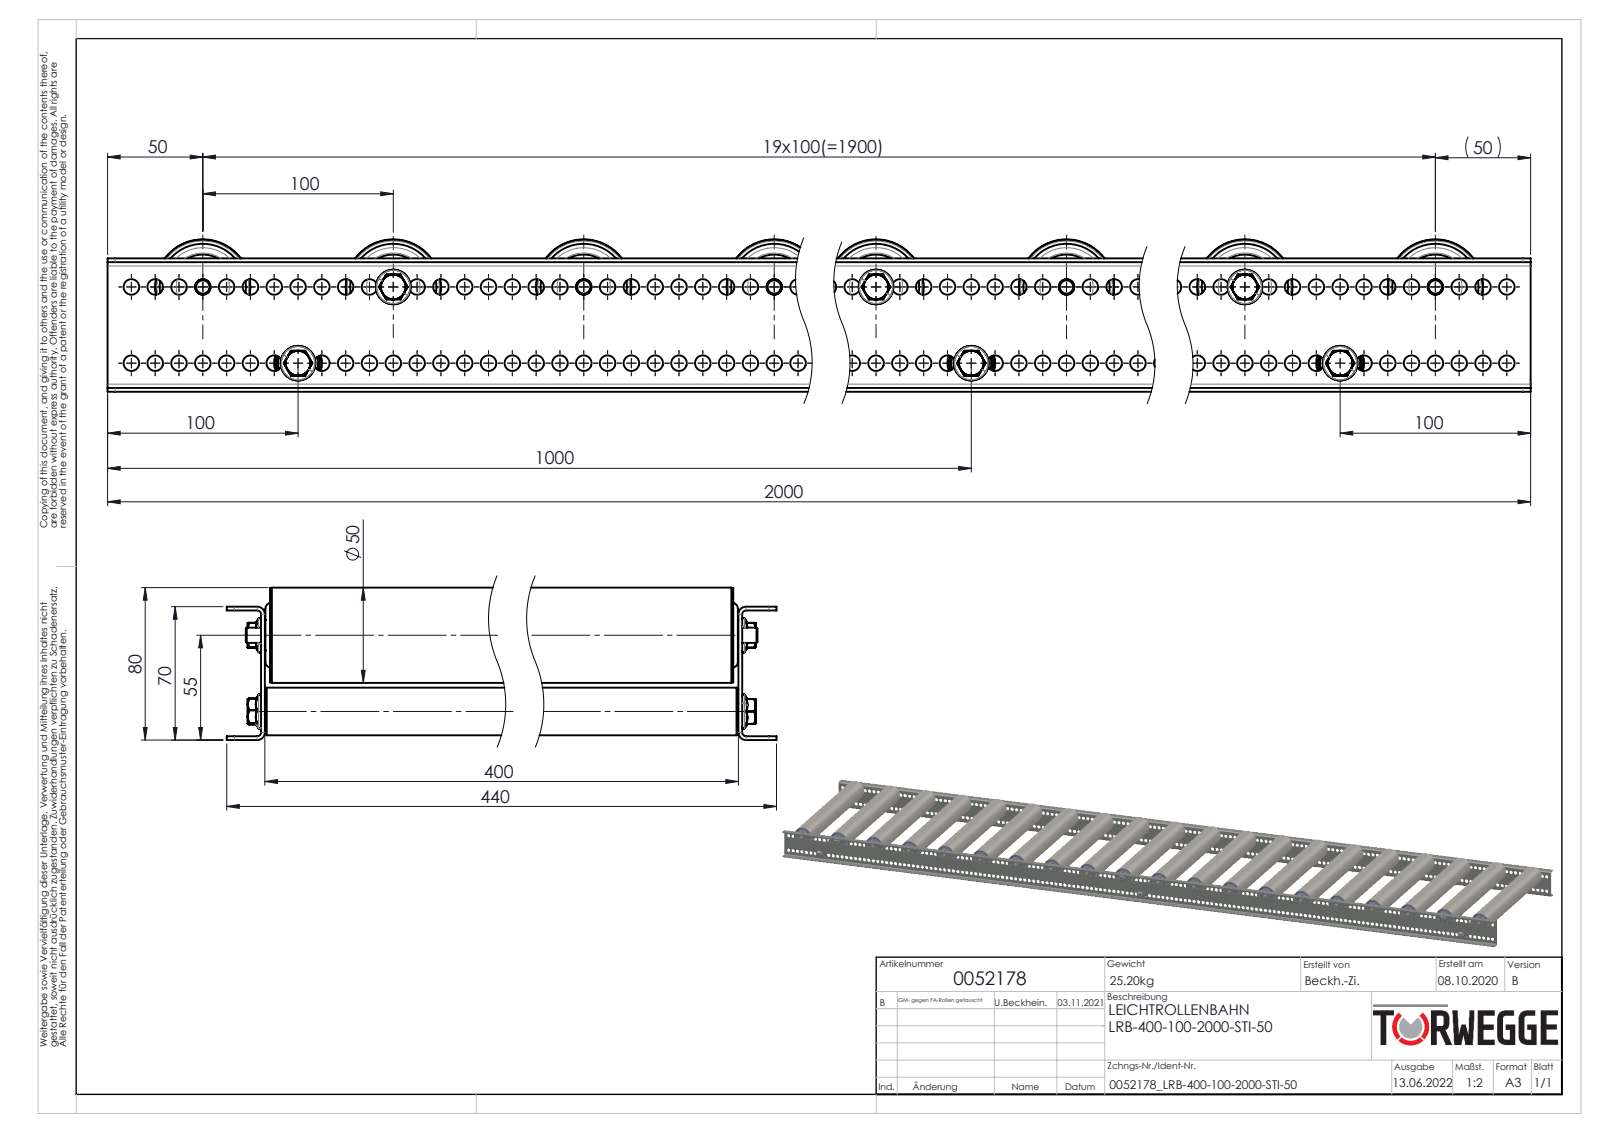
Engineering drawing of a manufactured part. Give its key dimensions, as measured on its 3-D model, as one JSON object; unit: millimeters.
{"part_name": "Tragrollenachse-Ø8_KFG_L=420; 0039780-Achse-ST-Ø12-KFG_IGM8-AL=400-TRG; 0039771_Tragrollenrohr-Ø50x1,5STI_KFG_EL400; 0026295_Typ-TRG_50x1,5-8 (+8 more)", "step_written_by": "SolidWorks 2020 (AUTOMOTIVE_DESIGN)", "units": "millimeters", "bodies": {"solids": 476, "faces": 8806, "planar": 1716, "cylindrical": 3328, "other": 3762}, "overall_size": [2000, 440, 80], "volume_mm3": 3622000, "surface_area_mm2": 4208000, "round_holes": [[8.2, 318], [17.1, 20], [18.5, 20], [27.7, 20], [45.3, 20], [47, 20], [7.6, 17], [6.8, 6], [12, 3], [12.2, 3], [19.2, 3], [21, 3]], "round_bosses_or_shafts": [[8, 23], [50, 20], [49.5, 20], [47.3, 20], [29.7, 20], [27.4, 20], [27.3, 20], [16, 20]], "partial_cylinders_radius": [[0.6, 34], [0.75, 34], [2.45, 34], [4.87, 17], [7, 17], [2.5, 12], [4, 8], [2, 4]], "face_to_face_distances": [2, 402, 68, 400, 404, 70, 66, 1, 2.3, 401.7], "hole_center_spacings": [12.5, 25, 37.5, 50, 62.5, 75, 87.5, 100]}
